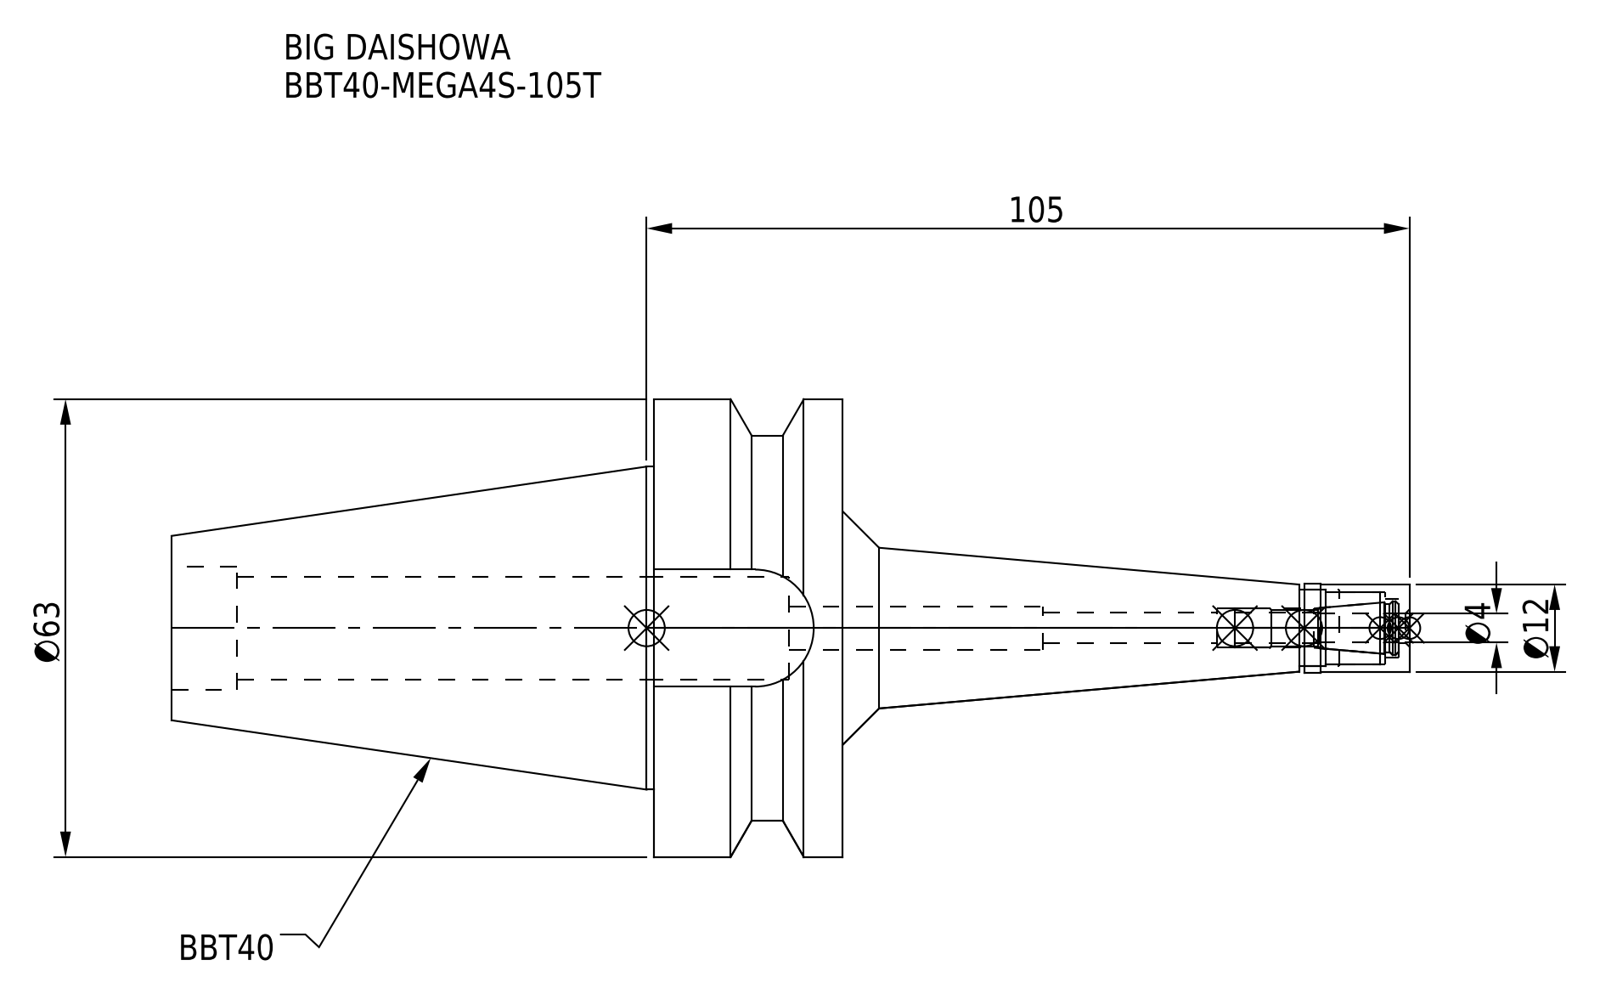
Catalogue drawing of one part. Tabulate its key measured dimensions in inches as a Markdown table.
| quantity | value |
| --- | --- |
| part name | BBT40-MEGA4S-105T_1.stp; BBT40-MEGA4S-105T; BBT40MS04105T-040_ASM.stp; DXF_TEMP_ASSY_ASM_4_ASM.stp (+3 more) |
| STEP written by | SolidWorks 2019 (CONFIG_CONTROL_DESIGN) |
| units | inches |
| bodies | 2 solids, 74 faces (22 planar, 38 cylindrical, 14 other) |
| overall size | 6.709 × 2.48 × 2.48 |
| volume | 8.399 in³ |
| surface area | 44.29 in² |
| round holes (diameter × count) | 0.161 × 1, 0.165 × 1, 0.213 × 1, 0.236 × 1, 0.315 × 1, 0.394 × 1, 0.413 × 1, 0.559 × 1, 0.669 × 1 |
| round bosses / shafts (diameter × count) | 2.48 × 1, 2.087 × 1, 1.75 × 1, 0.484 × 1, 0.472 × 1 |
| partial cylindrical surfaces (radius × count) | 0.317 × 1 |
| main face-to-face distances | 1.024, 1.772, 3.638, 2.614, 0.634, 0.291, 0.732, 3.346, 3.071, 3.362 |
